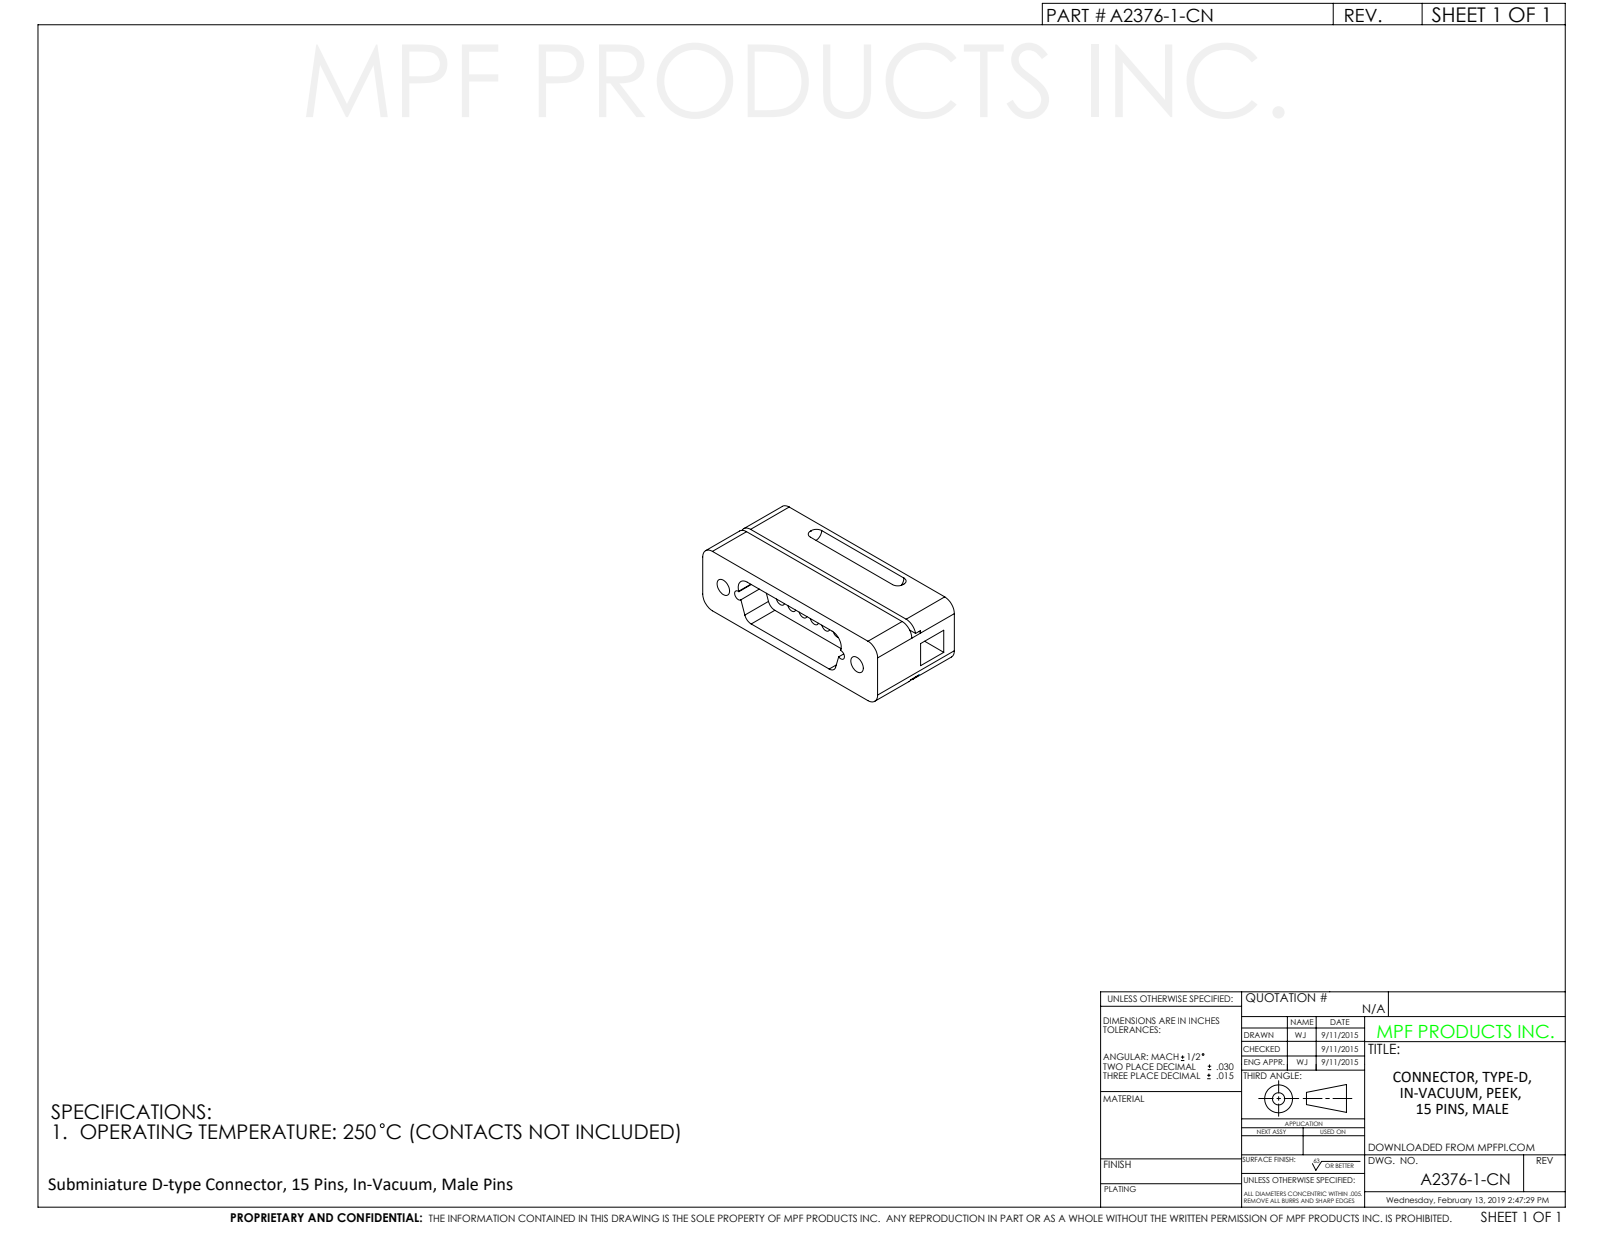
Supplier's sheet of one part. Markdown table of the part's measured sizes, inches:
| quantity | value |
| --- | --- |
| part name | A2376-1-CN |
| STEP written by | SolidWorks 2012 (CONFIG_CONTROL_DESIGN) |
| units | inches |
| bodies | 0 solids, 146 faces (47 planar, 95 cylindrical, 4 other) |
| overall size | 1.7 × 0.746 × 0.5 |
| round holes (diameter × count) | 0.08 × 15, 0.07 × 2, 0.079 × 2, 0.08 × 2, 0.083 × 2, 0.084 × 2, 0.11 × 2, 0.121 × 2, 0.15 × 2, 0.076 × 1 |
| round bosses / shafts (diameter × count) | 0.139 × 2 |
| partial cylindrical surfaces (radius × count) | 0.094 × 5, 0.055 × 2, 0.066 × 2, 0.089 × 2, 0.203 × 1 |
| main face-to-face distances | 0.5, 0.746, 0.516, 0.23, 0.414, 0.102, 0.332, 0.375, 0.039, 0.141 |
| hole center spacings | 0.22, 0.131, 0.11, 0.135, 0.33, 0.11, 0.55, 0.201 |
